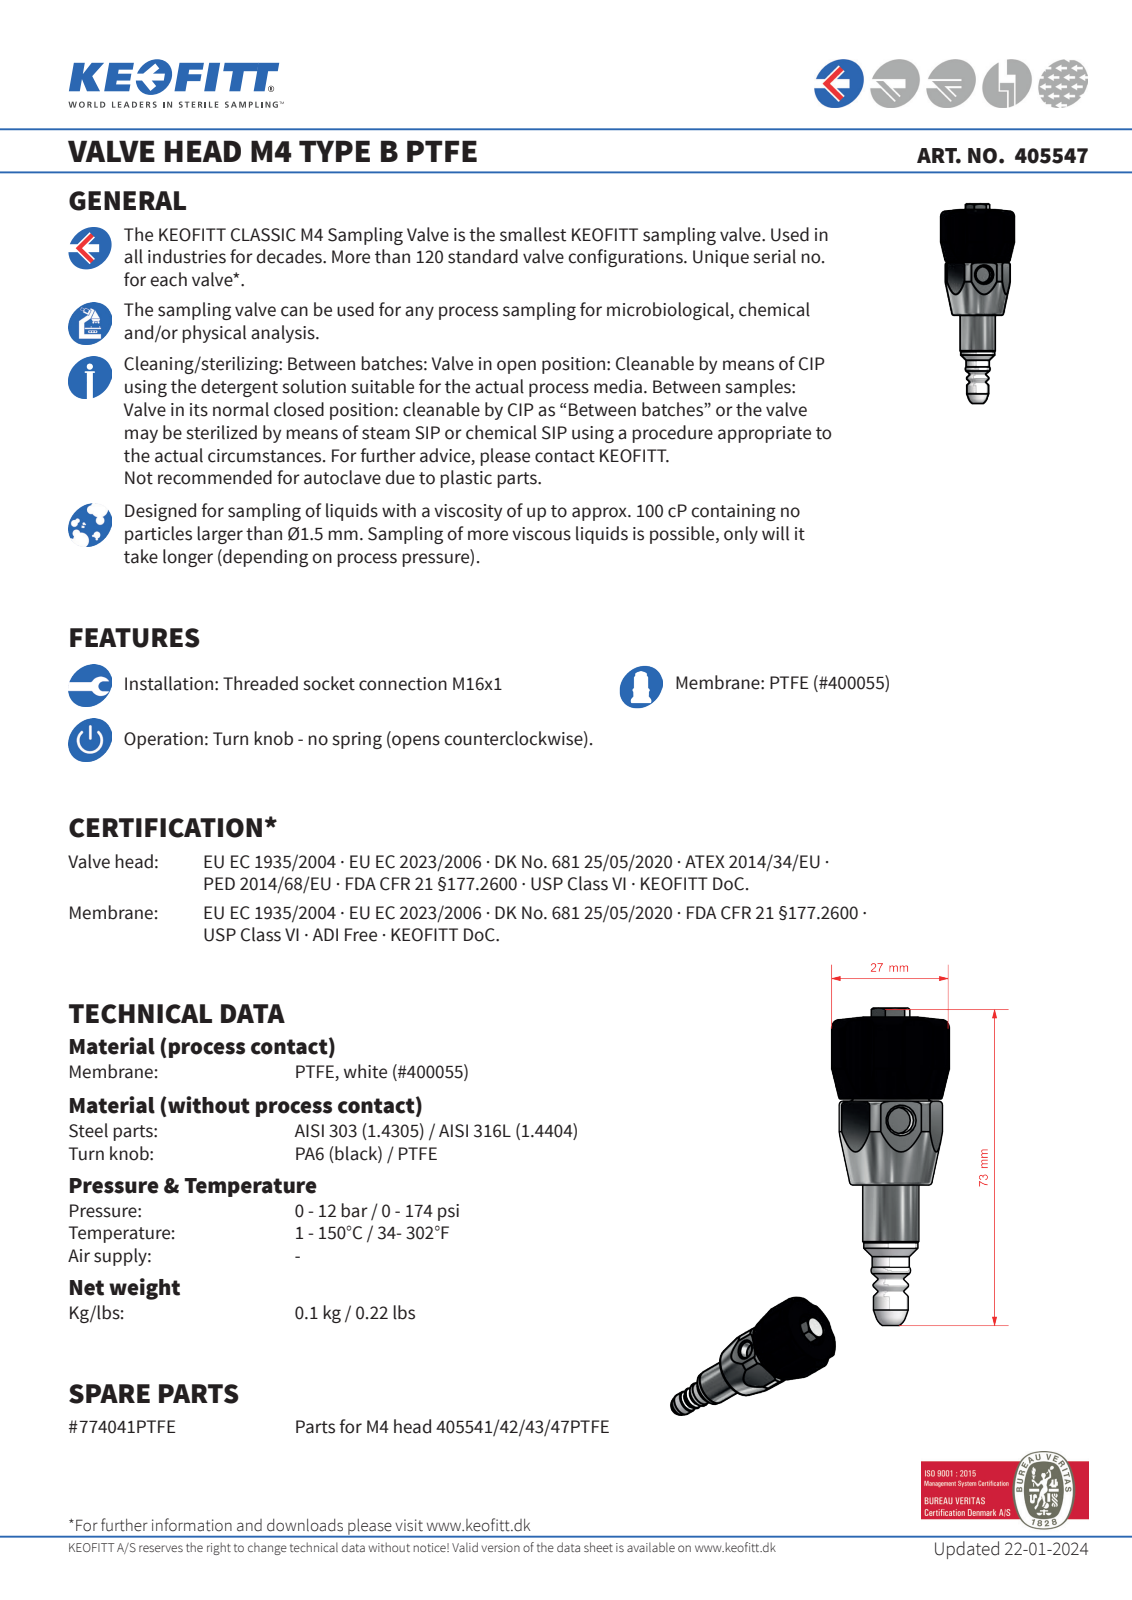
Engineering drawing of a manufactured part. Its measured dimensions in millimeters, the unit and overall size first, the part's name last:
Units: millimetres
Overall size (bounding box): 73.2 × 28 × 27.95
Round holes (diameter × count): ⌀3.05 ×1, ⌀6.1 ×1, ⌀10.1 ×1, ⌀12.5 ×1, ⌀20.5 ×1
Round bosses / shafts (diameter × count): ⌀17 ×1, ⌀13 ×1, ⌀12.5 ×1, ⌀10 ×1, ⌀8.6 ×1, ⌀8.05 ×1, ⌀3 ×1
Partial cylindrical surfaces — rounded edges, fillets, slot ends (radius × count): R6 ×6, R4.64 ×1, R10 ×1, R12 ×1, R14 ×1
Main face-to-face distances: 0.5, 22, 21.99, 1, 16.6, 17.1, 17.6, 36.79, 20.19, 19.69
Hole centre spacings: 1
Volume: 19 945 mm³ · Surface area: 5 966 mm²
Bodies: 1 solid, 115 faces (27 planar, 32 cylindrical, 56 other)
STEP written by: Autodesk Inventor 2008 (AUTOMOTIVE_DESIGN)
